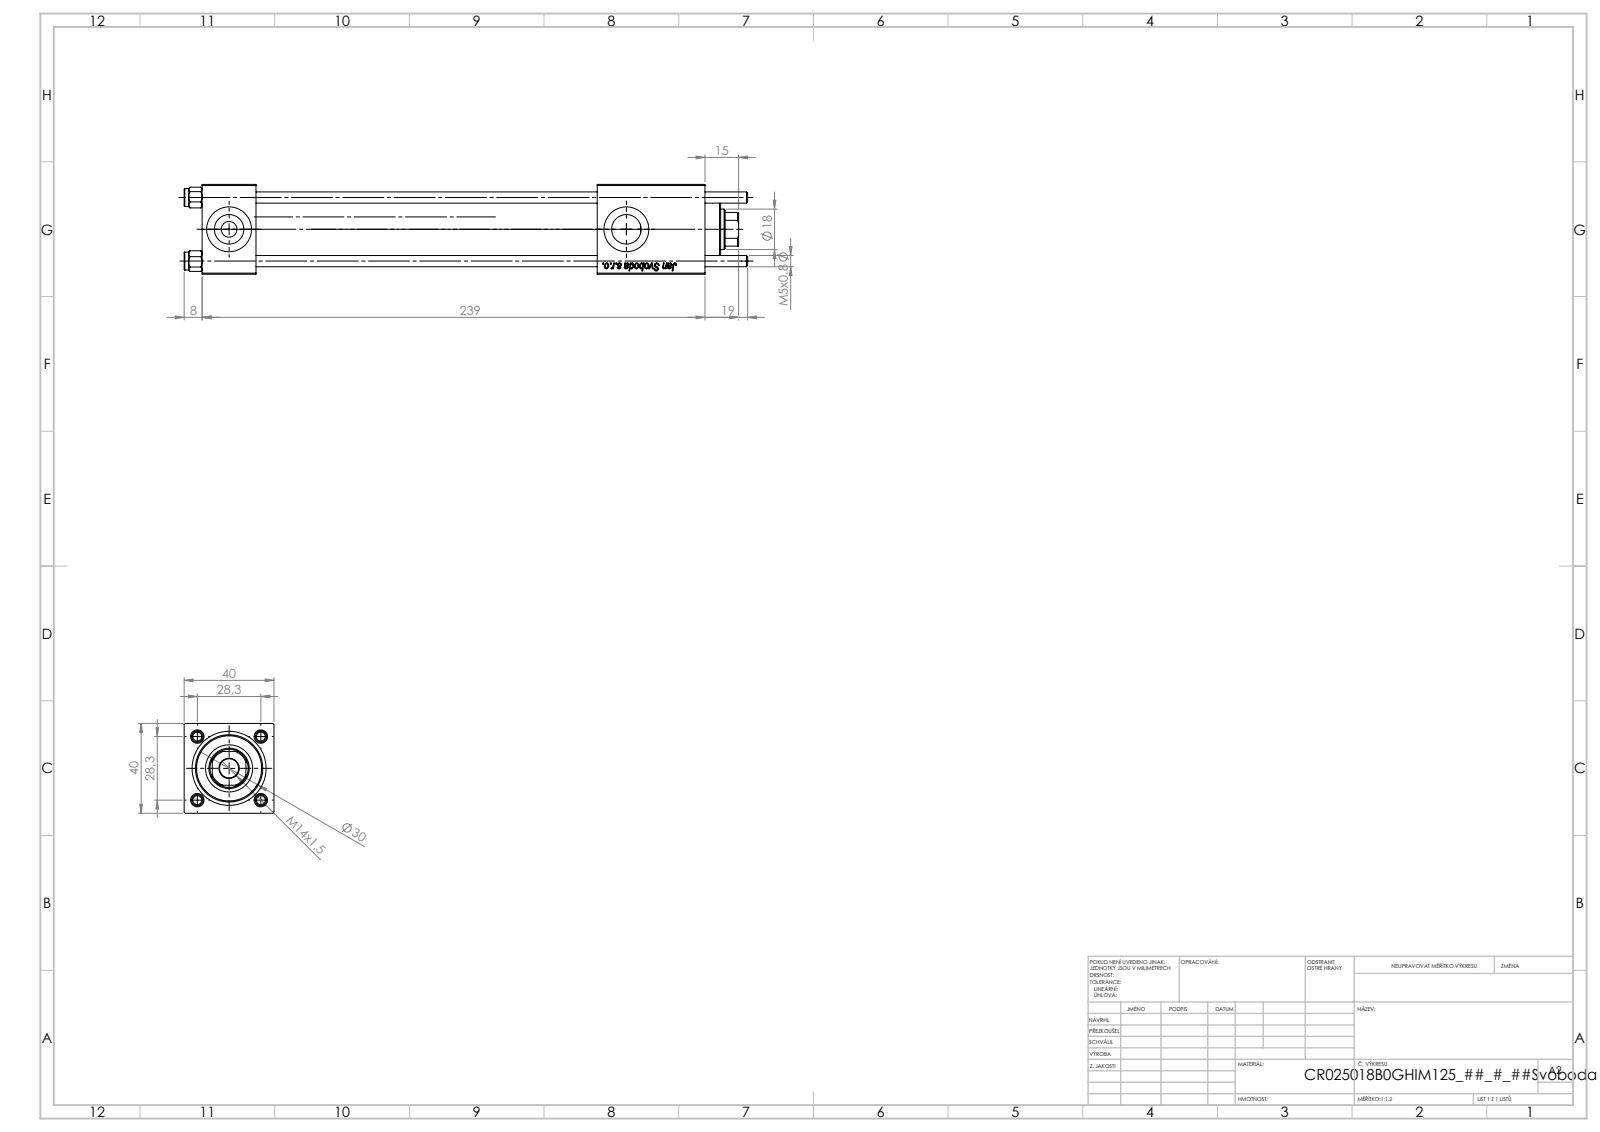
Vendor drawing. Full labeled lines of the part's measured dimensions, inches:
Part name (STEP PRODUCT): V215CR_B-1; V215CR_VCP_B; NUT_M5_B; V215_VC_A (+1 more)
STEP written by: SolidWorks 2019 (CONFIG_CONTROL_DESIGN)
Units: inches
Bodies: 11 solids, 1152 faces (428 planar, 76 cylindrical, 648 other)
Overall size (bounding box): 9.882 × 1.575 × 1.575
Volume: 13.13 in³ · Surface area: 142.4 in²
Round holes (diameter × count): ⌀0.197 ×4, ⌀0.787 ×3, ⌀0.276 ×2, ⌀0.518 ×2, ⌀0.335 ×1, ⌀0.709 ×1, ⌀0.827 ×1, ⌀0.984 ×1, ⌀1.181 ×1
Round bosses / shafts (diameter × count): ⌀0.315 ×4, ⌀1.22 ×1
Partial cylindrical surfaces — rounded edges, fillets, slot ends (radius × count): R0.335 ×1
Main face-to-face distances: 1.575, 0.945, 6.929, 5.984, 7.689, 6.744, 0.76, 8.819, 7.874, 1.89
Hole centre spacings: 0.788, 1.114, 1.576, 6.969
